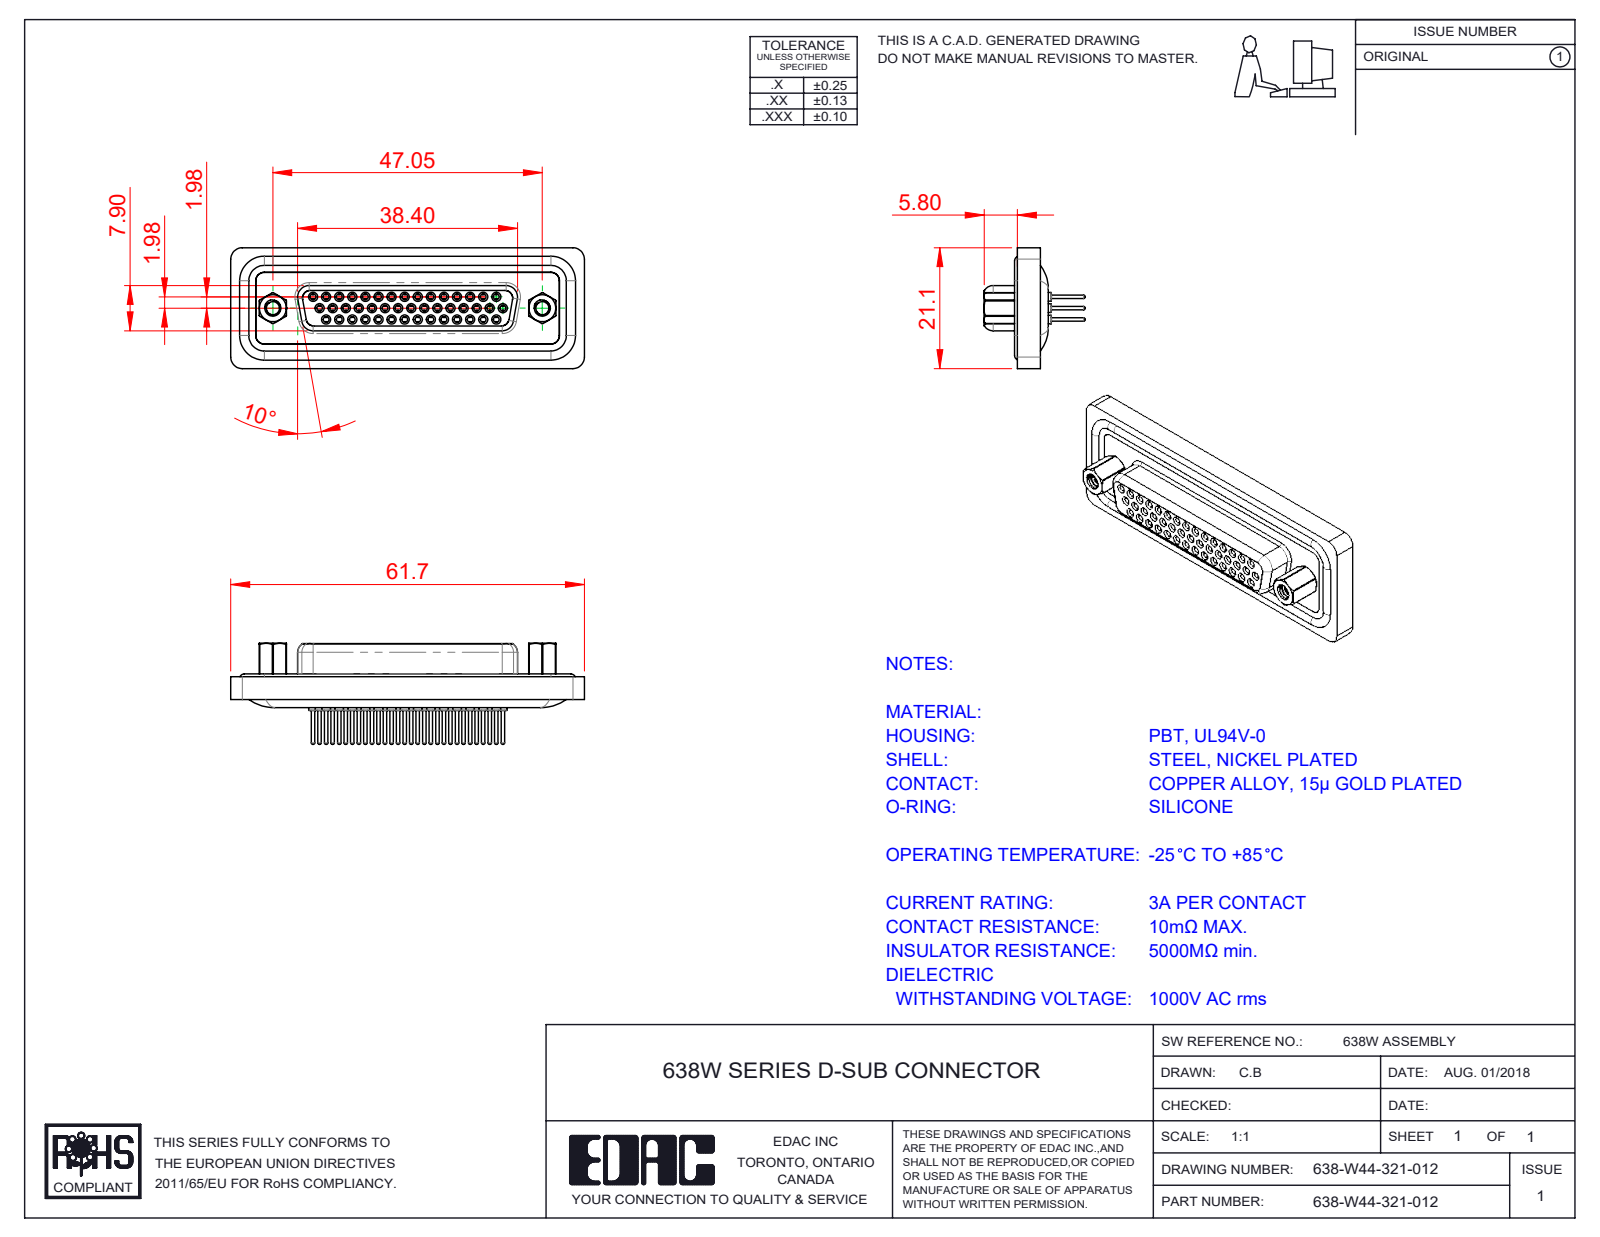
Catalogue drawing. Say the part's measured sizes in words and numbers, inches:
The part is named "638W Waterproof Housing_44 Contacts; 638W 4-40 Hex Standoff; 638W Shell_44 Contacts; 638W 4-40 Threaded Rivet (+5 more)". Its 3-D file was written by "SolidWorks 2016 (CONFIG_CONTROL_DESIGN)". It is 52 solids with 2929 faces: 761 planar, 1140 cylindrical and 1028 other. Overall it measures 2.431 by 0.831 by 0.695 inches. Its volume is 0.437 cubic inches and its surface area 24.31 square inches. Round holes: 44 of diameter 0.039, 44 of diameter 0.043, 44 of diameter 0.059, 44 of diameter 0.067, 44 of diameter 0.071, 44 of diameter 0.079, 2 of diameter 0.089, 2 of diameter 0.09, 2 of diameter 0.157, 2 of diameter 0.189, 2 of diameter 0.197. Round bosses or shafts: 48 of diameter 0.063, 44 of diameter 0.087, 44 of diameter 0.024, 23 of diameter 0.059, 2 of diameter 0.193, 2 of diameter 0.11, 1 of diameter 0.197. Partial cylindrical surfaces (rounded edges, fillets, slot ends): 14 of radius 0.079, 13 of radius 0.059, 9 of radius 0.053, 6 of radius 0.106, 4 of radius 0.02, 4 of radius 0.035, 4 of radius 0.063, 4 of radius 0.069. The main face-to-face distances are 0.016, 0.071, 0.114, 0.063, 0.098, 0.043, 0.293, 0.537, 0.02, 0.222. The hole center spacings are 0.09, 0.09, 0.156, 0.18, 0.324, 0.27, 0.45, 0.59.
